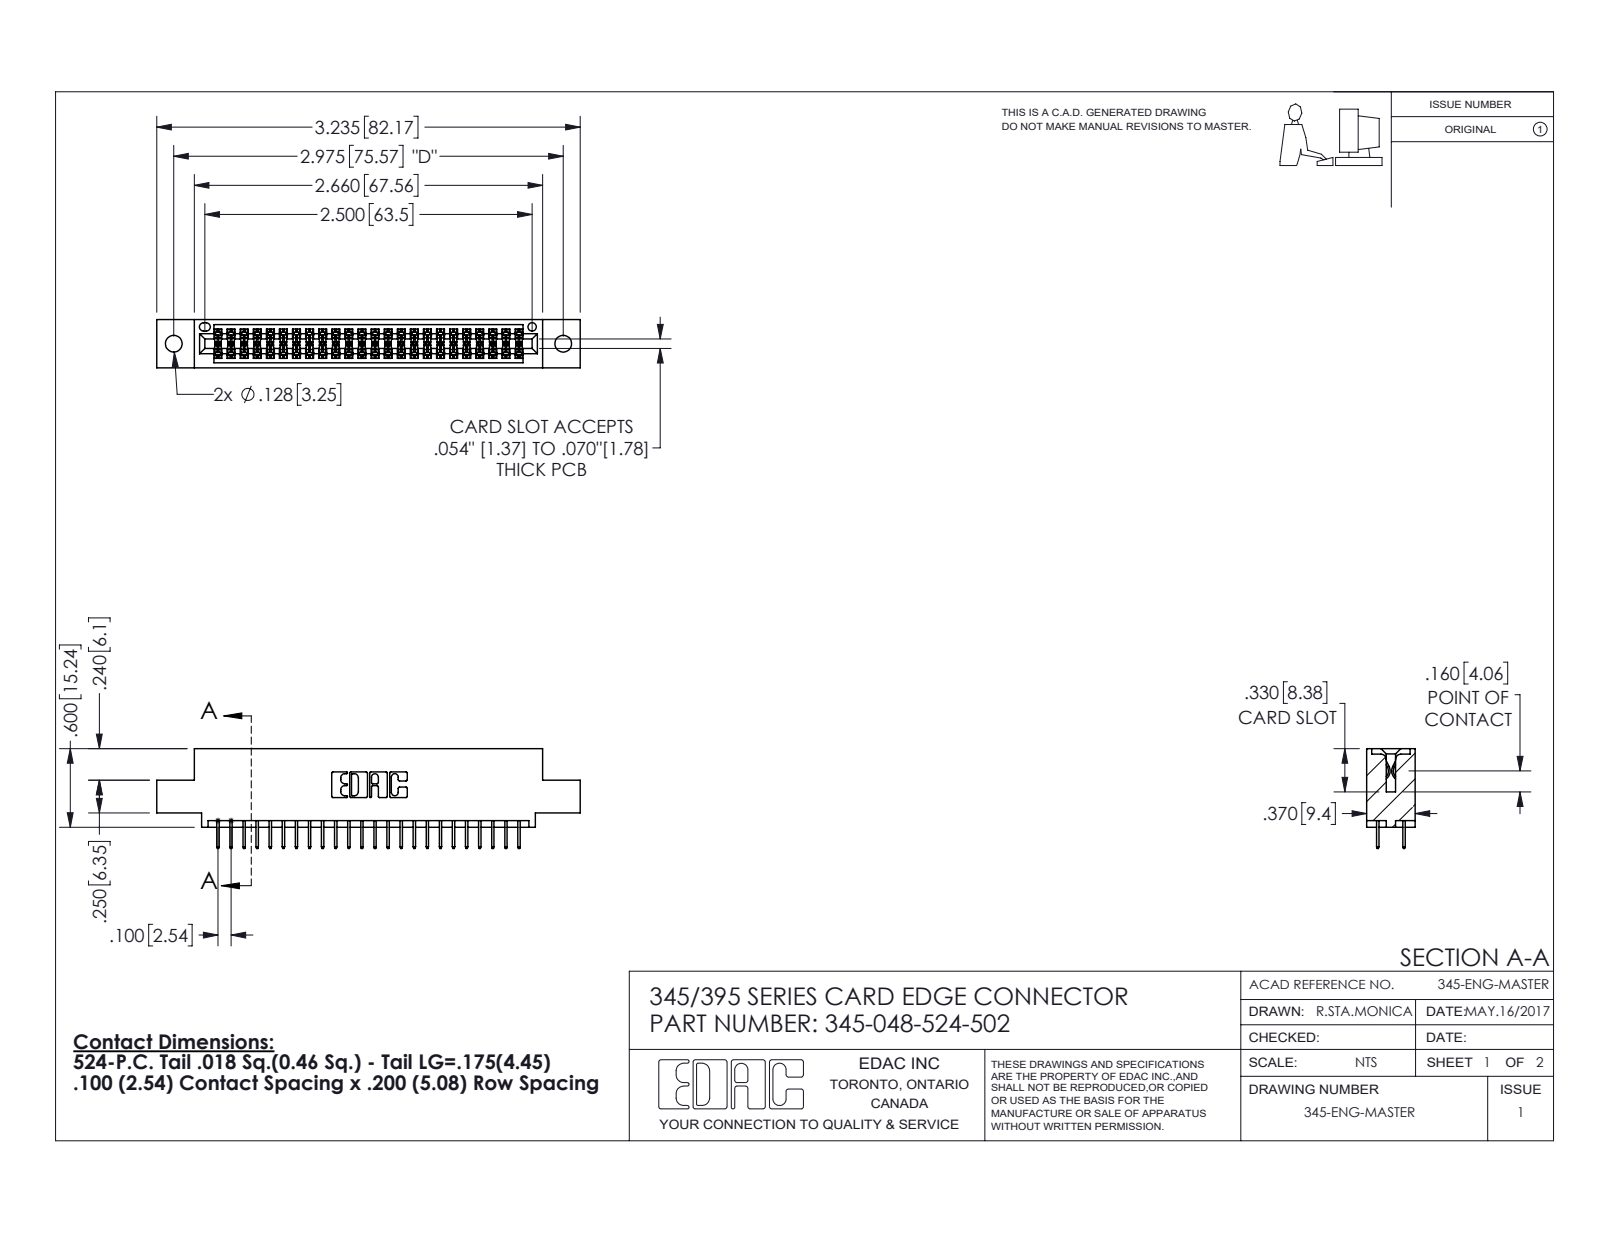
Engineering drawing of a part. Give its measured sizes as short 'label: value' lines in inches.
name: 345-048-524-502; 345-292-001_345-293-124; 345 Part_0.110 Offset - 0.128 Dia
written by: SolidWorks 2016 (CONFIG_CONTROL_DESIGN)
unit: in
bodies: 49 solids, 2722 faces (1956 planar, 766 cylindrical, 0 other)
size: 3.235 × 0.762 × 0.37
volume: 0.466 in³; area: 16.37 in²
holes: 2× ⌀0.128, 1× ⌀0.064
rounds: 72× R0.006, 22× R0.01, 6× R0.007, 6× R0.031, 3× R0.026, 2× R0.014, 2× R0.019, 2× R0.022
face distances: 0.072, 0.298, 0.2, 0.37, 0.098, 0.272, 0.025, 0.225, 0.072, 0.175
hole spacings: 0.27, 2.741, 2.975
